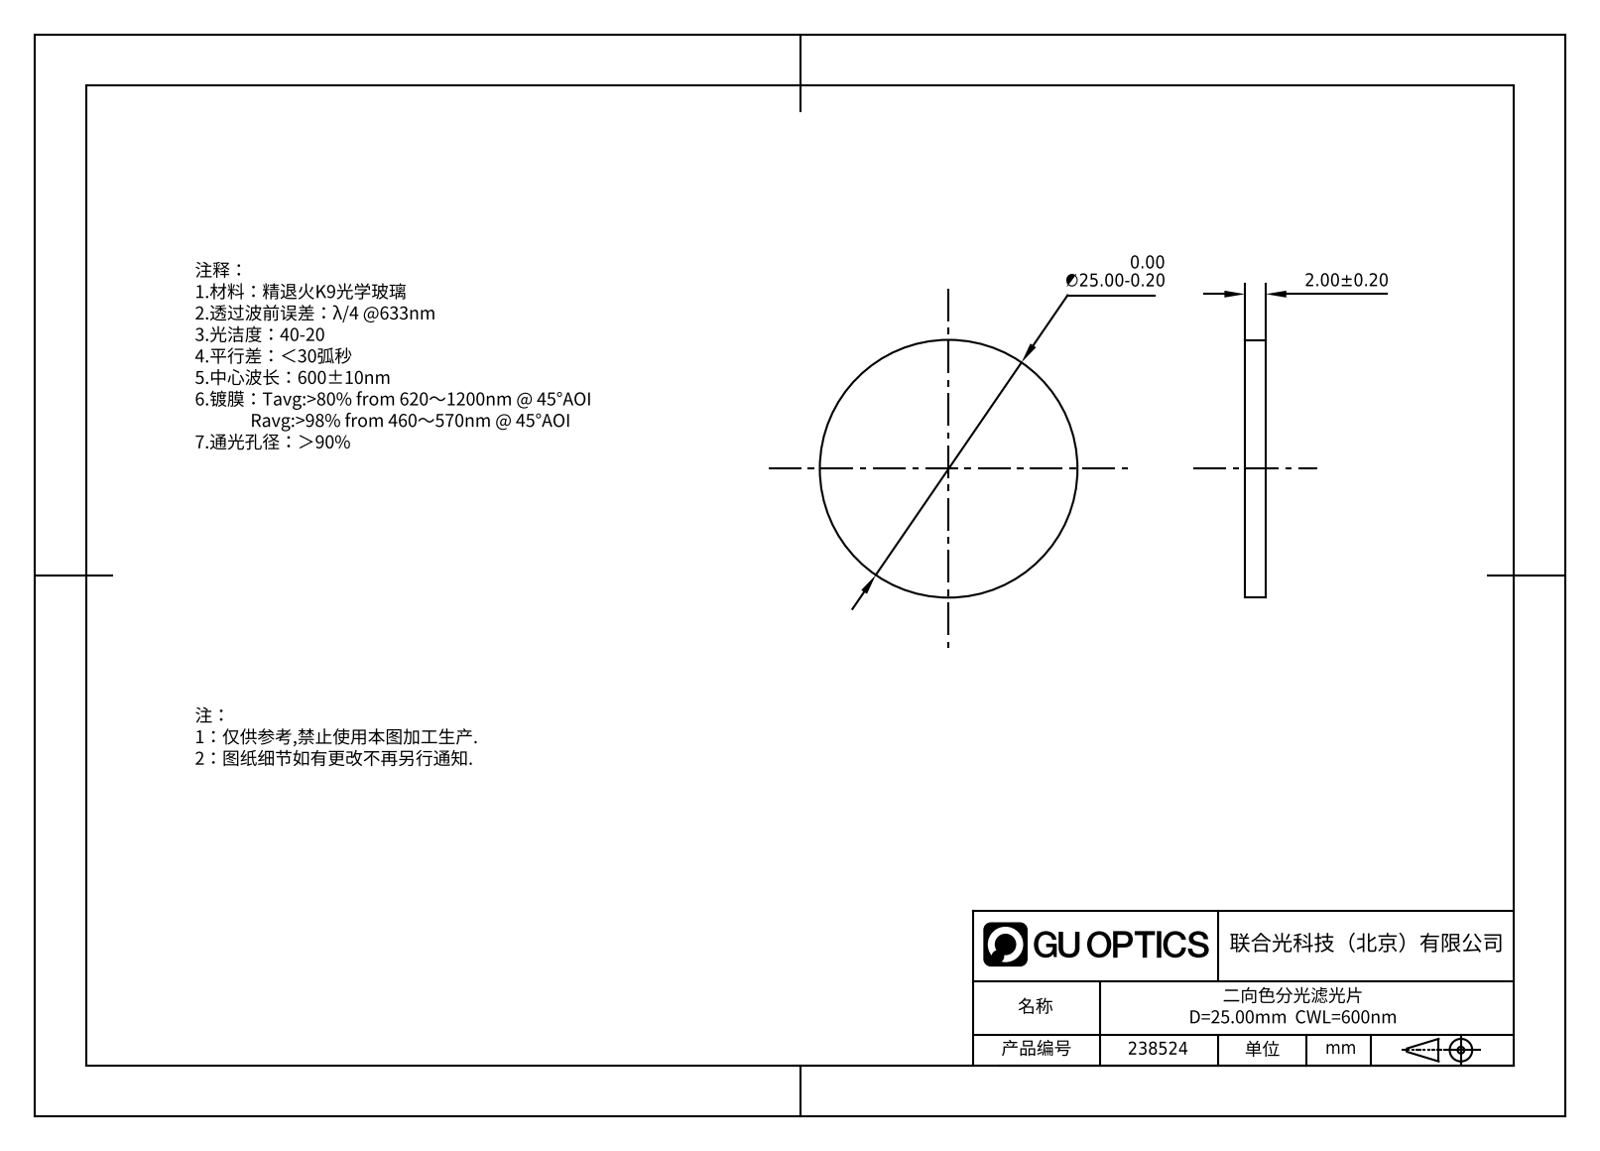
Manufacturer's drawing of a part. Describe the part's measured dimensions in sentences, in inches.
The part is named "238520". Its 3-D file was written by "SolidWorks 2016 (AUTOMOTIVE_DESIGN)". It is 1 solid with 4 faces: 2 planar, 2 cylindrical and 0 other. Overall it measures 0.984 by 0.984 by 0.079 inches. Its volume is 0.06 cubic inches and its surface area 1.765 square inches. Round bosses or shafts: 1 of diameter 0.984. The main face-to-face distances are 0.079.
